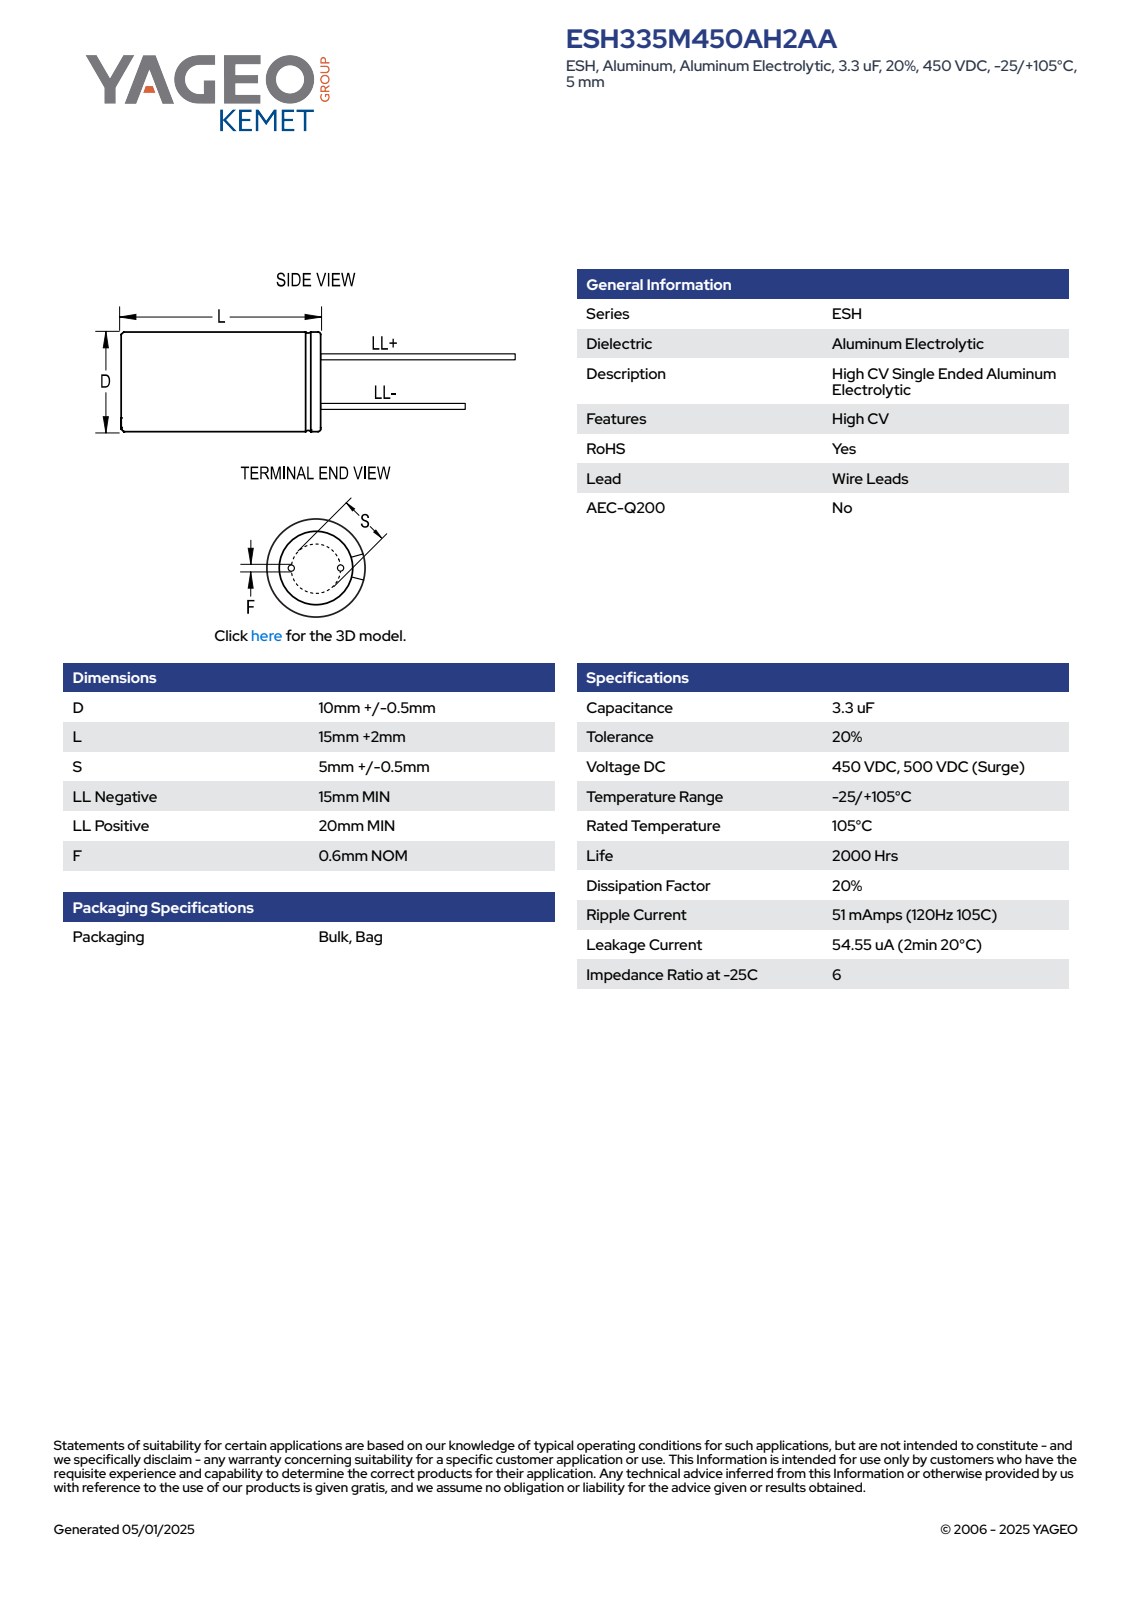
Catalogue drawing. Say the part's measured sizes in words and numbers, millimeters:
The part is named "CAR_KLP_10 X 16_D10.5L17S5F0.6". Its 3-D file was written by "SolidWorks 2014 (AUTOMOTIVE_DESIGN)". It is 4 solids with 75 faces: 61 planar, 8 cylindrical and 6 other. Overall it measures 37.01 by 10.5 by 10.5 millimeters. Its volume is 1 470 cubic millimeters and its surface area 825 square millimeters. Round bosses or shafts: 2 of diameter 0.6, 1 of diameter 10.5. The main face-to-face distances are 17, 17.01, 32.01, 37.01, 32, 37, 15, 20, 5, 1.41.
